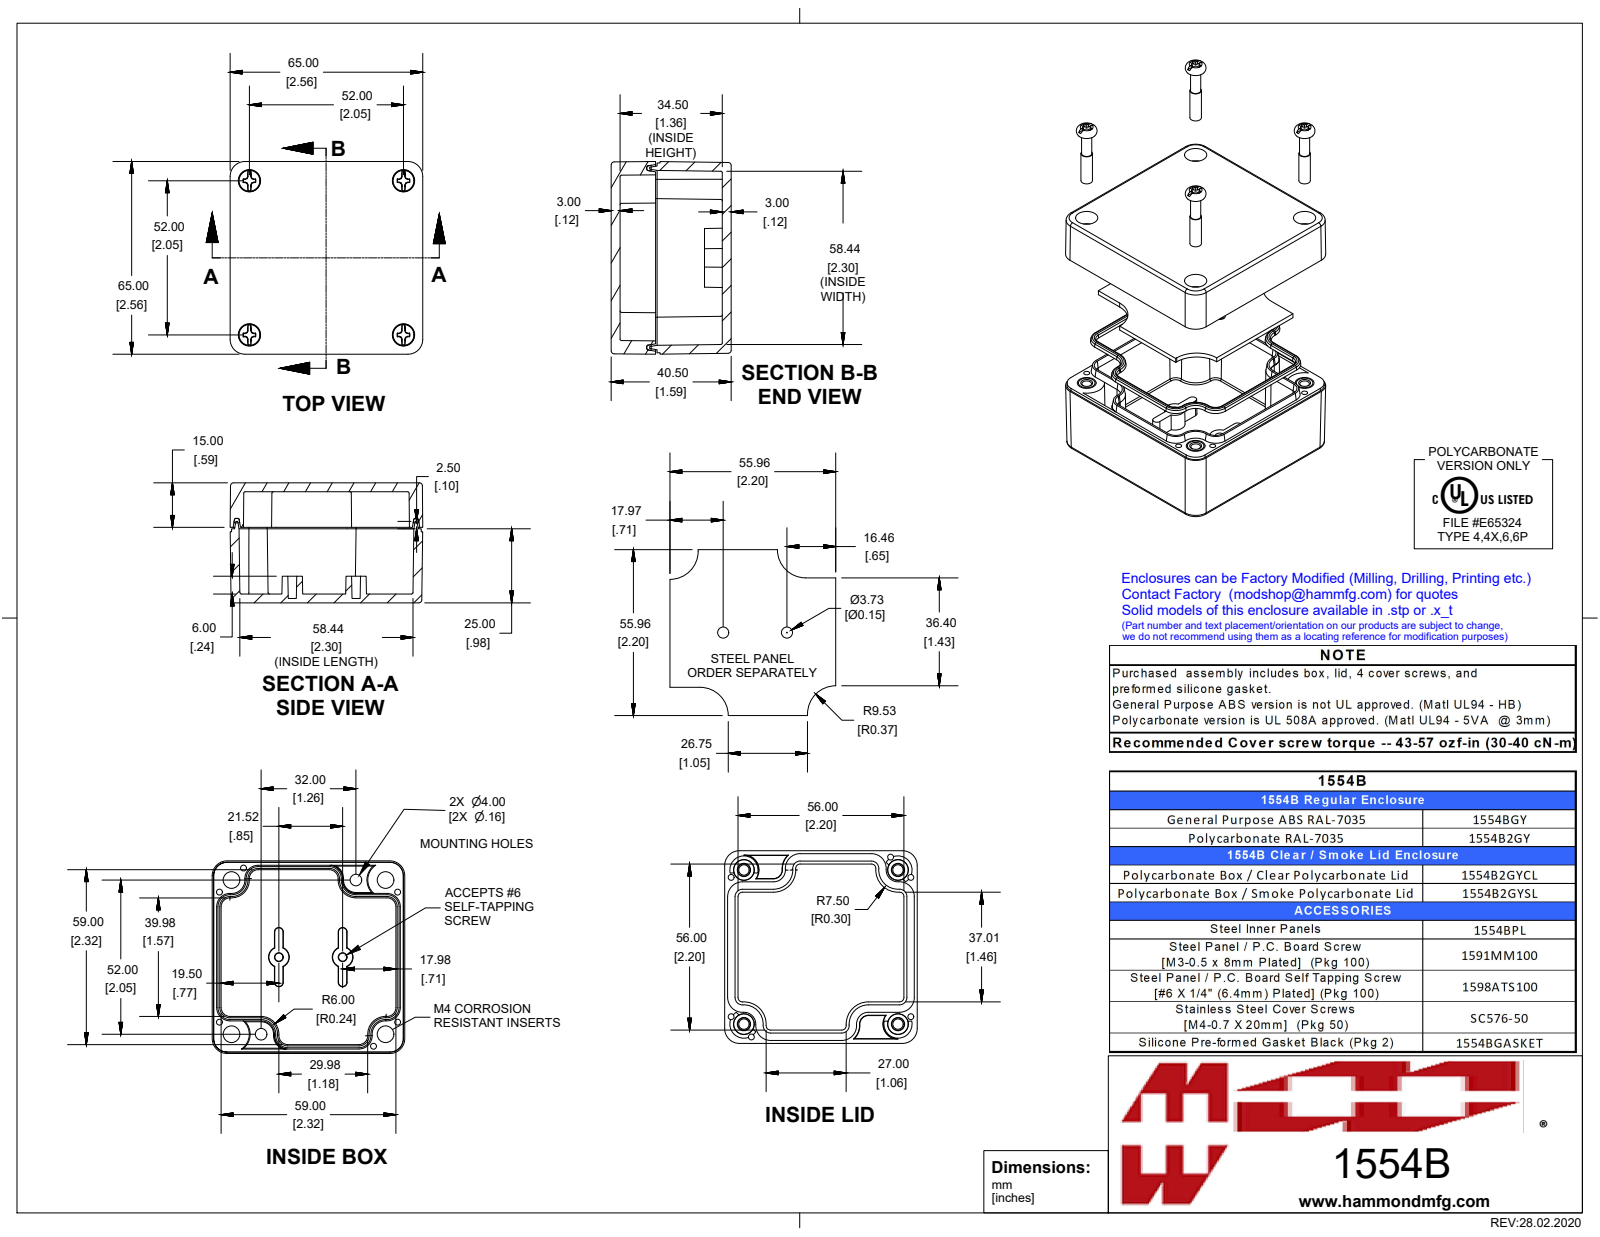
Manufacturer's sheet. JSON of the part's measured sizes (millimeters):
{"part_name": "1554BGY", "step_written_by": "SolidWorks 2019 (AUTOMOTIVE_DESIGN)", "units": "millimeters", "bodies": {"solids": 11, "faces": 654, "planar": 254, "cylindrical": 124, "other": 276}, "overall_size": [65, 65, 40.5], "volume_mm3": 61730, "surface_area_mm2": 46470, "round_holes": [[2, 12], [3.3, 4], [3.5, 4]], "round_bosses_or_shafts": [[6.4, 4], [5.5, 4], [5.3, 4], [3.9, 4], [3.4, 4]], "partial_cylinders_radius": [[0.5, 32], [1, 8], [5, 8], [3.5, 4], [4.7, 4]], "face_to_face_distances": [3, 37.5, 40.5, 34.5, 1.5, 4.5, 12.5, 2, 25.5, 12], "hole_center_spacings": [5, 49.7, 56.4, 75, 5.7, 10.7, 52, 52.6]}
